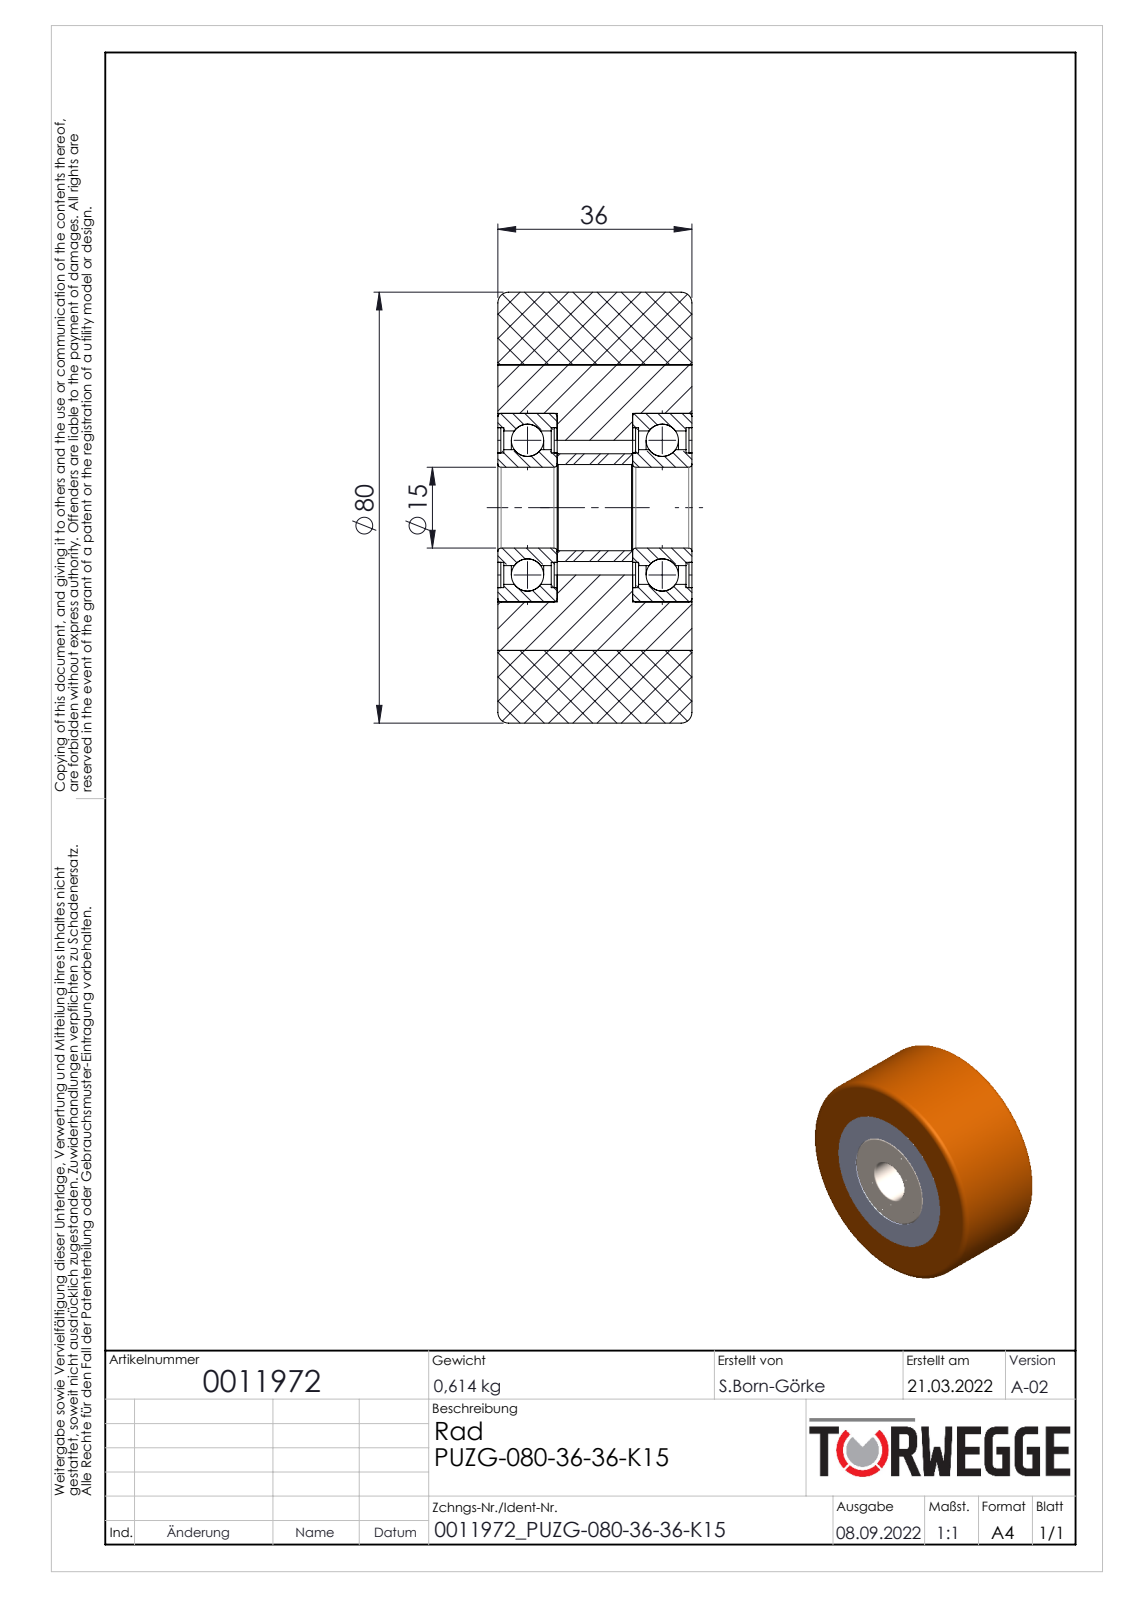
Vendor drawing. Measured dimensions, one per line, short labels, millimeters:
name: 0011972
written by: SolidWorks 2020 (AUTOMOTIVE_DESIGN)
unit: mm
bodies: 13 solids, 152 faces (32 planar, 72 cylindrical, 48 other)
size: 80 × 80 × 36
volume: 168 762 mm³; area: 50 291 mm²
holes: 1× ⌀15, 1× ⌀16, 1× ⌀20.3, 1× ⌀25, 1× ⌀28.48, 1× ⌀29.7, 1× ⌀35, 1× ⌀53
bosses: 1× ⌀80, 1× ⌀21.52, 1× ⌀20
face distances: 36, 25, 11, 0.55, 10.45, 14, 9.9, 25.55, 24.45, 35.45
